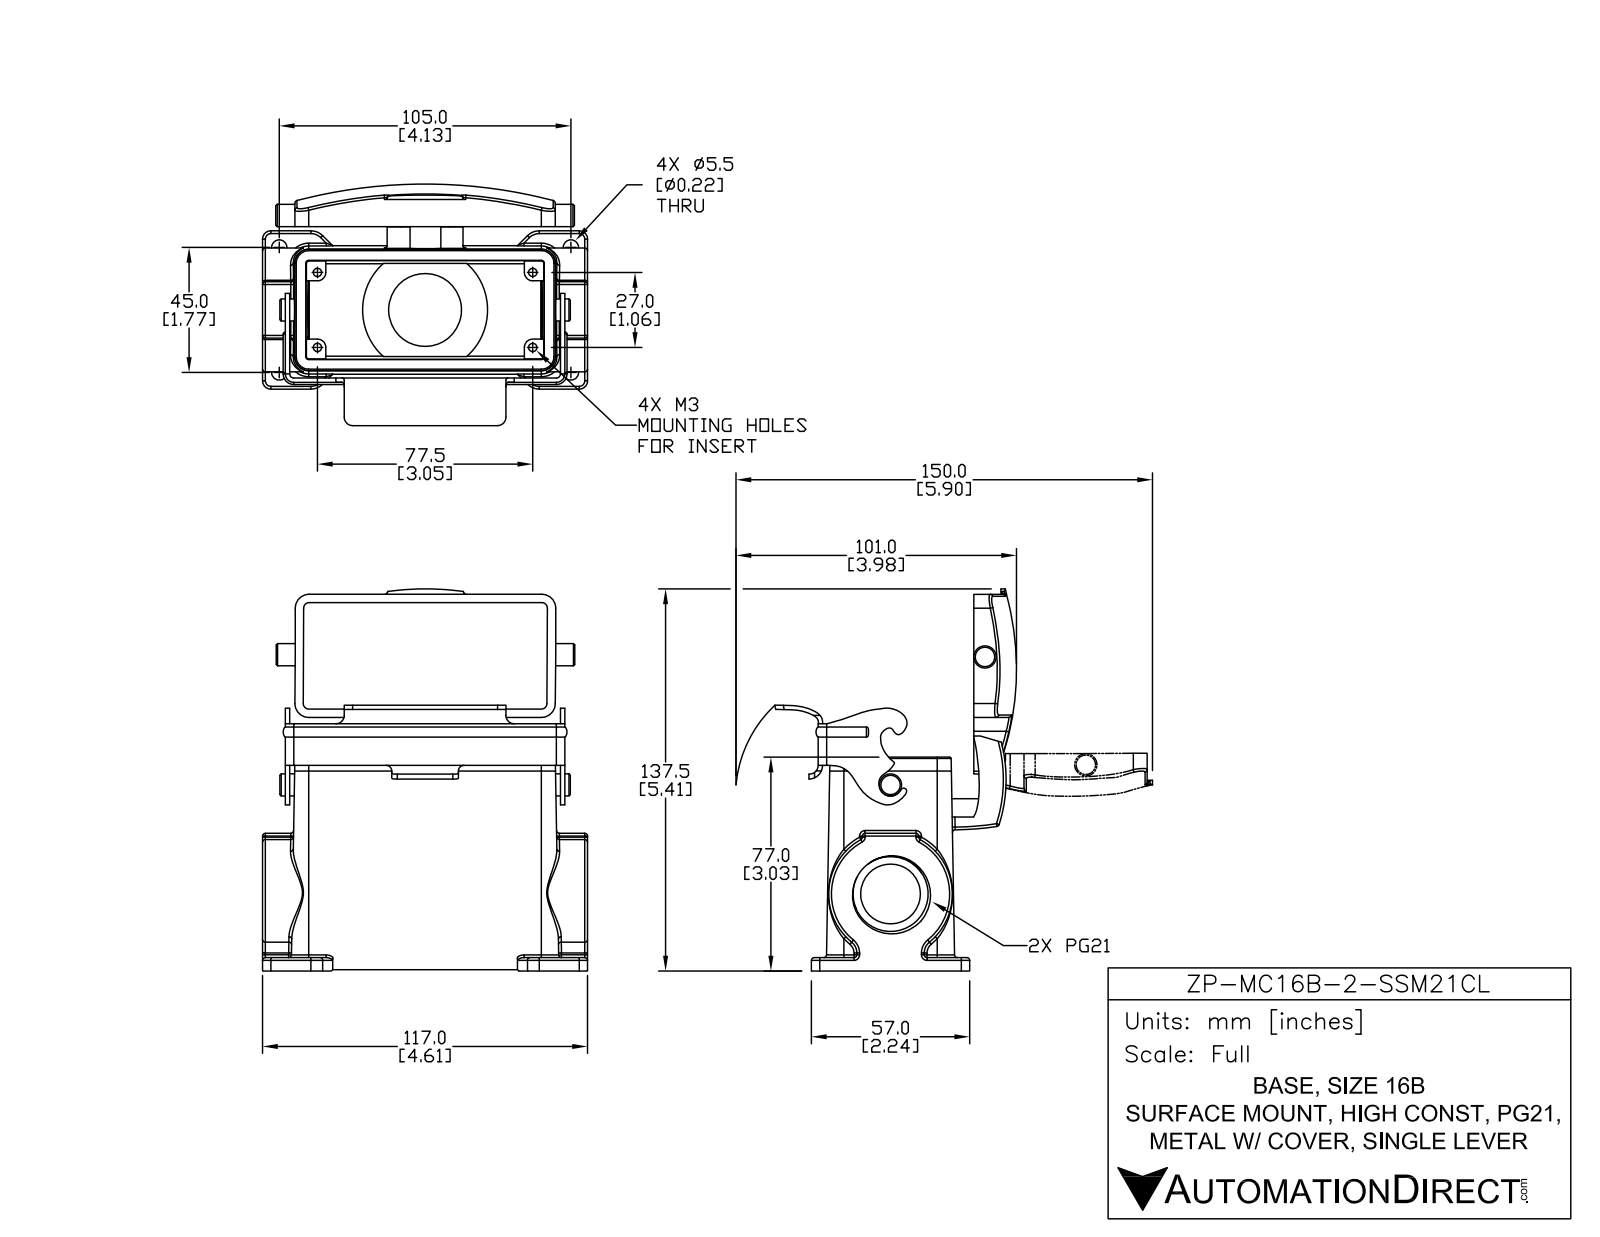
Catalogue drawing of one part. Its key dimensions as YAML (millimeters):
part_name: "ZP-MC16B-2-SSM21CL"
step_written_by: "SolidWorks 2014 (AUTOMOTIVE_DESIGN)"
units: millimeters
bodies: {solids: 3, faces: 510, planar: 160, cylindrical: 202, other: 148}
overall_size: [136.13, 117, 86.98]
volume: 191281
surface_area: 82840
round_holes:
  - {diameter: 3, count: 4}
  - {diameter: 5.5, count: 4}
  - {diameter: 2, count: 1}
  - {diameter: 21.5, count: 1}
  - {diameter: 26.23, count: 1}
  - {diameter: 27, count: 1}
round_bosses_or_shafts:
  - {diameter: 8, count: 1}
  - {diameter: 7.95, count: 1}
partial_cylinders:
  - {radius: 1, count: 46}
  - {radius: 3, count: 12}
  - {radius: 2, count: 8}
  - {radius: 5, count: 8}
  - {radius: 0.5, count: 4}
  - {radius: 6, count: 4}
  - {radius: 1.5, count: 2}
  - {radius: 3.06, count: 2}
face_to_face_distances: [39.67, 0.5, 1.56, 3, 6.4, 5.9, 40.5, 72.15, 9.75, 35.1]
hole_center_spacings: [16.43, 38.54, 41.03, 57.12, 91.69, 98.09, 27, 45]
